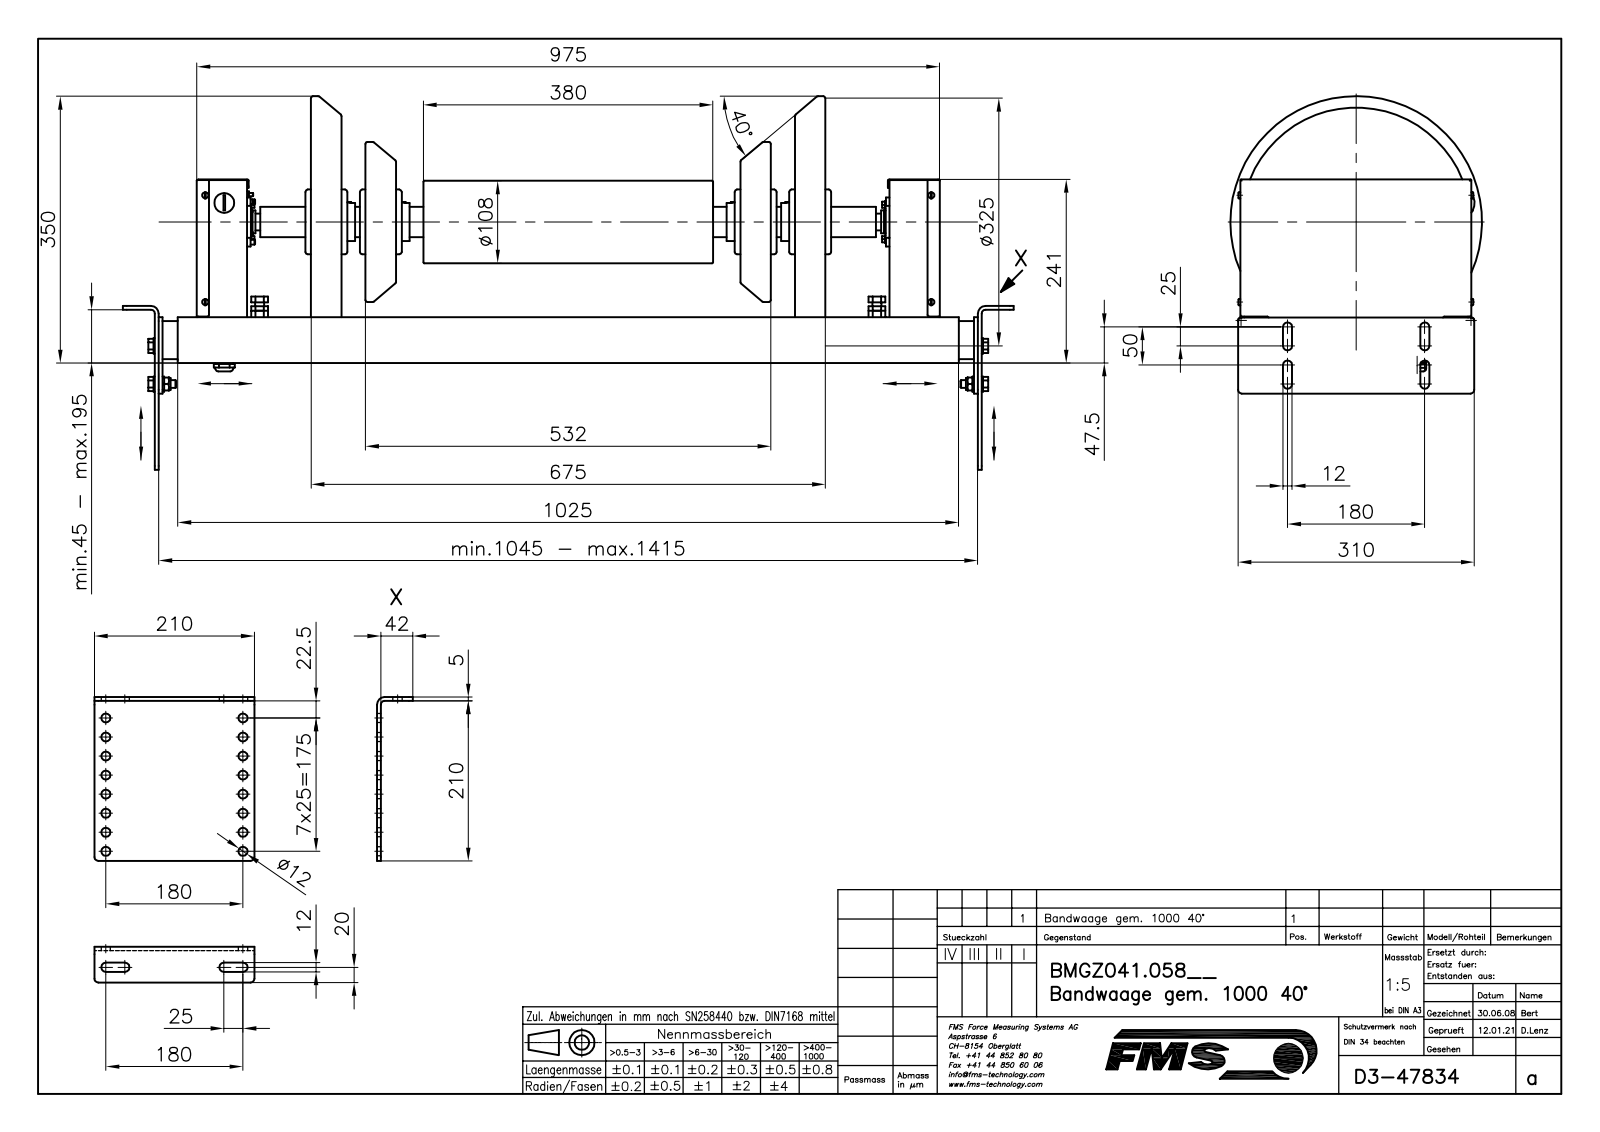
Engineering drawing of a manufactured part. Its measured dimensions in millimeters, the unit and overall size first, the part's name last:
Units: millimetres
Overall size (bounding box): 1169 × 490 × 330
Round holes (diameter × count): ⌀12 ×17, ⌀5 ×6, ⌀3.5 ×4, ⌀4.9 ×4, ⌀6.4 ×4, ⌀6.91 ×4, ⌀8.68 ×4, ⌀8.75 ×4, ⌀10 ×4, ⌀10.5 ×4, ⌀10.68 ×4, ⌀14.8 ×4
Round bosses / shafts (diameter × count): ⌀12 ×11, ⌀8.2 ×8, ⌀4.2 ×8, ⌀20 ×6, ⌀10 ×6, ⌀8 ×6, ⌀5 ×5, ⌀16 ×4
Partial cylindrical surfaces — rounded edges, fillets, slot ends (radius × count): R2 ×34, R1 ×24, R4 ×16, R5 ×16, R6 ×12, R3.5 ×8, R2.25 ×6, R0.5 ×4
Main face-to-face distances: 4, 5, 1, 51, 270, 36, 56, 3, 50, 8
Hole centre spacings: 25, 181.73, 50, 186.82, 75, 195, 100, 180
Volume: 9 186 000 mm³ · Surface area: 3 875 000 mm²
Bodies: 179 solids, 2992 faces (1435 planar, 1078 cylindrical, 479 other)
Part name (STEP PRODUCT): B47834_STP; B50108; 6KT-SCHRAUBE_M12X30; ZYL_SCHR__M4X8 (+8 more)
STEP written by: Mechanical Desktop 2009 (CONFIG_CONTROL_DESIGN)
